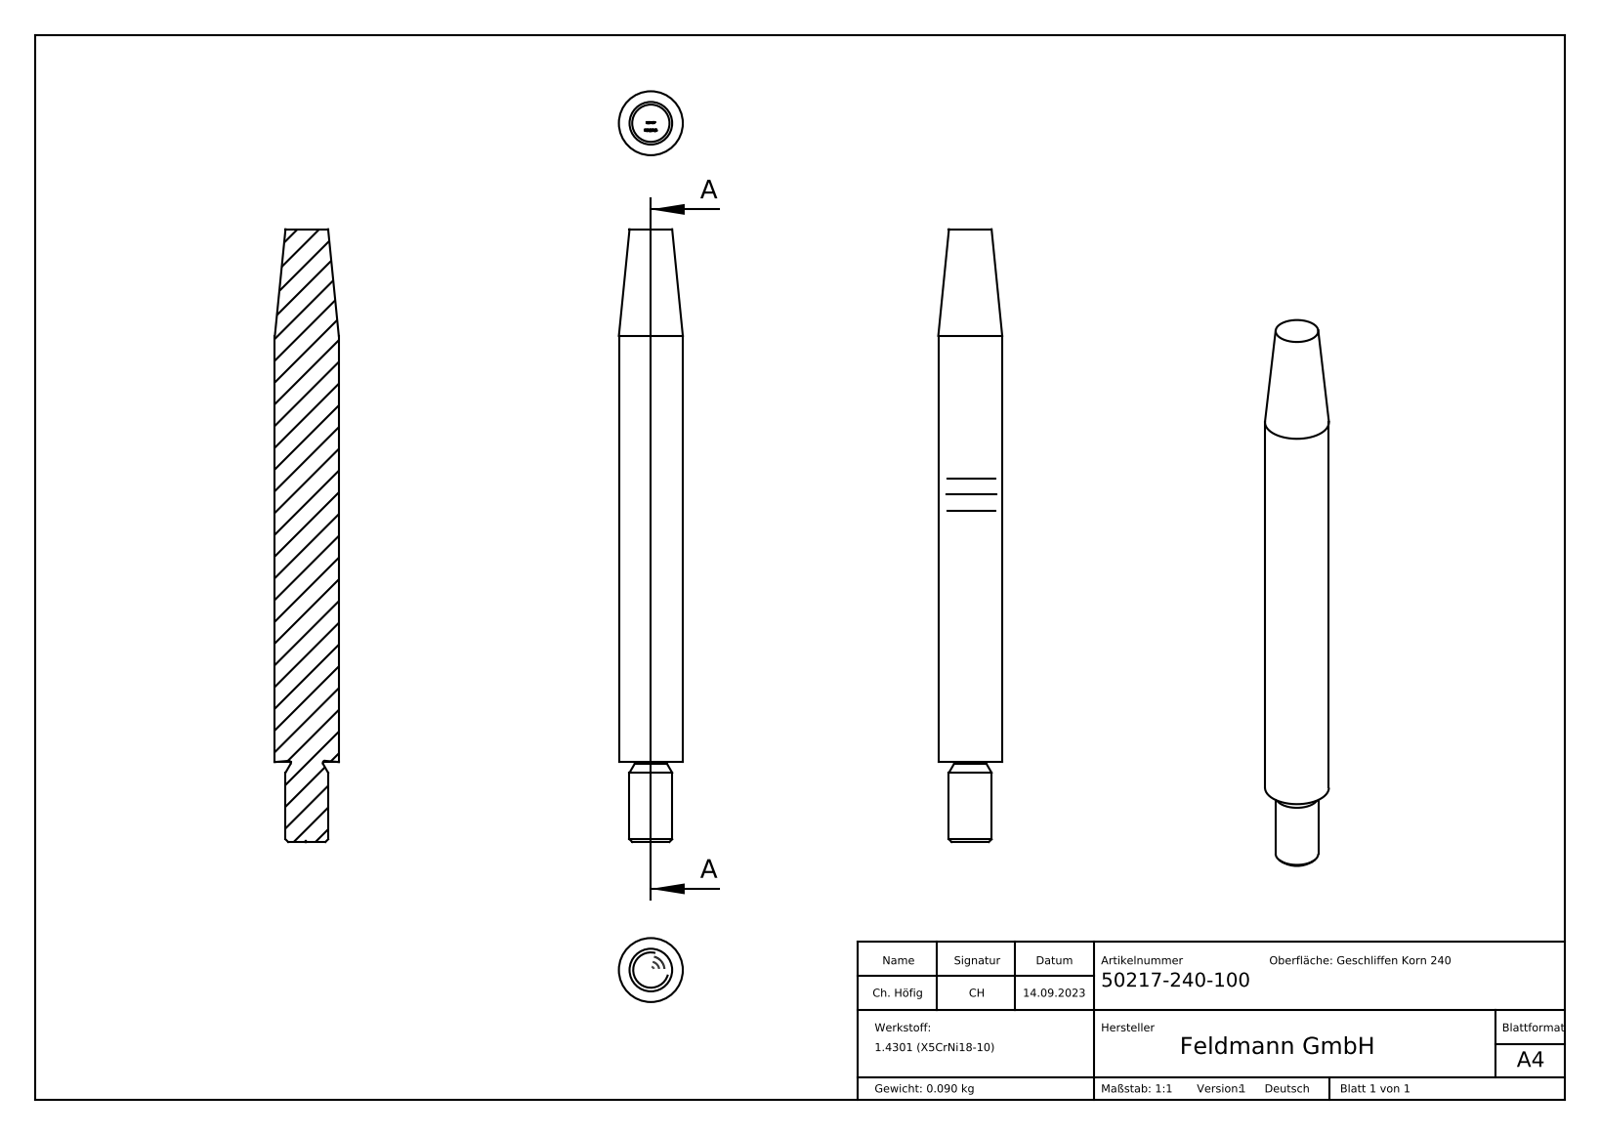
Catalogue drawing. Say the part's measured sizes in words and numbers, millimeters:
The part is named "50217-240-100". Its 3-D file was written by "SolidWorks 2018 (CONFIG_CONTROL_DESIGN)". It is 1 solid with 246 faces: 145 planar, 2 cylindrical and 99 other. Overall it measures 115 by 12 by 12 millimeters. Its volume is 11 356 cubic millimeters and its surface area 4 204 square millimeters. Round bosses or shafts: 1 of diameter 12, 1 of diameter 8. The main face-to-face distances are 115, 114.9, 0.33, 0.54, 1.44, 0.94, 0.79, 0.59, 1.33, 0.91.
